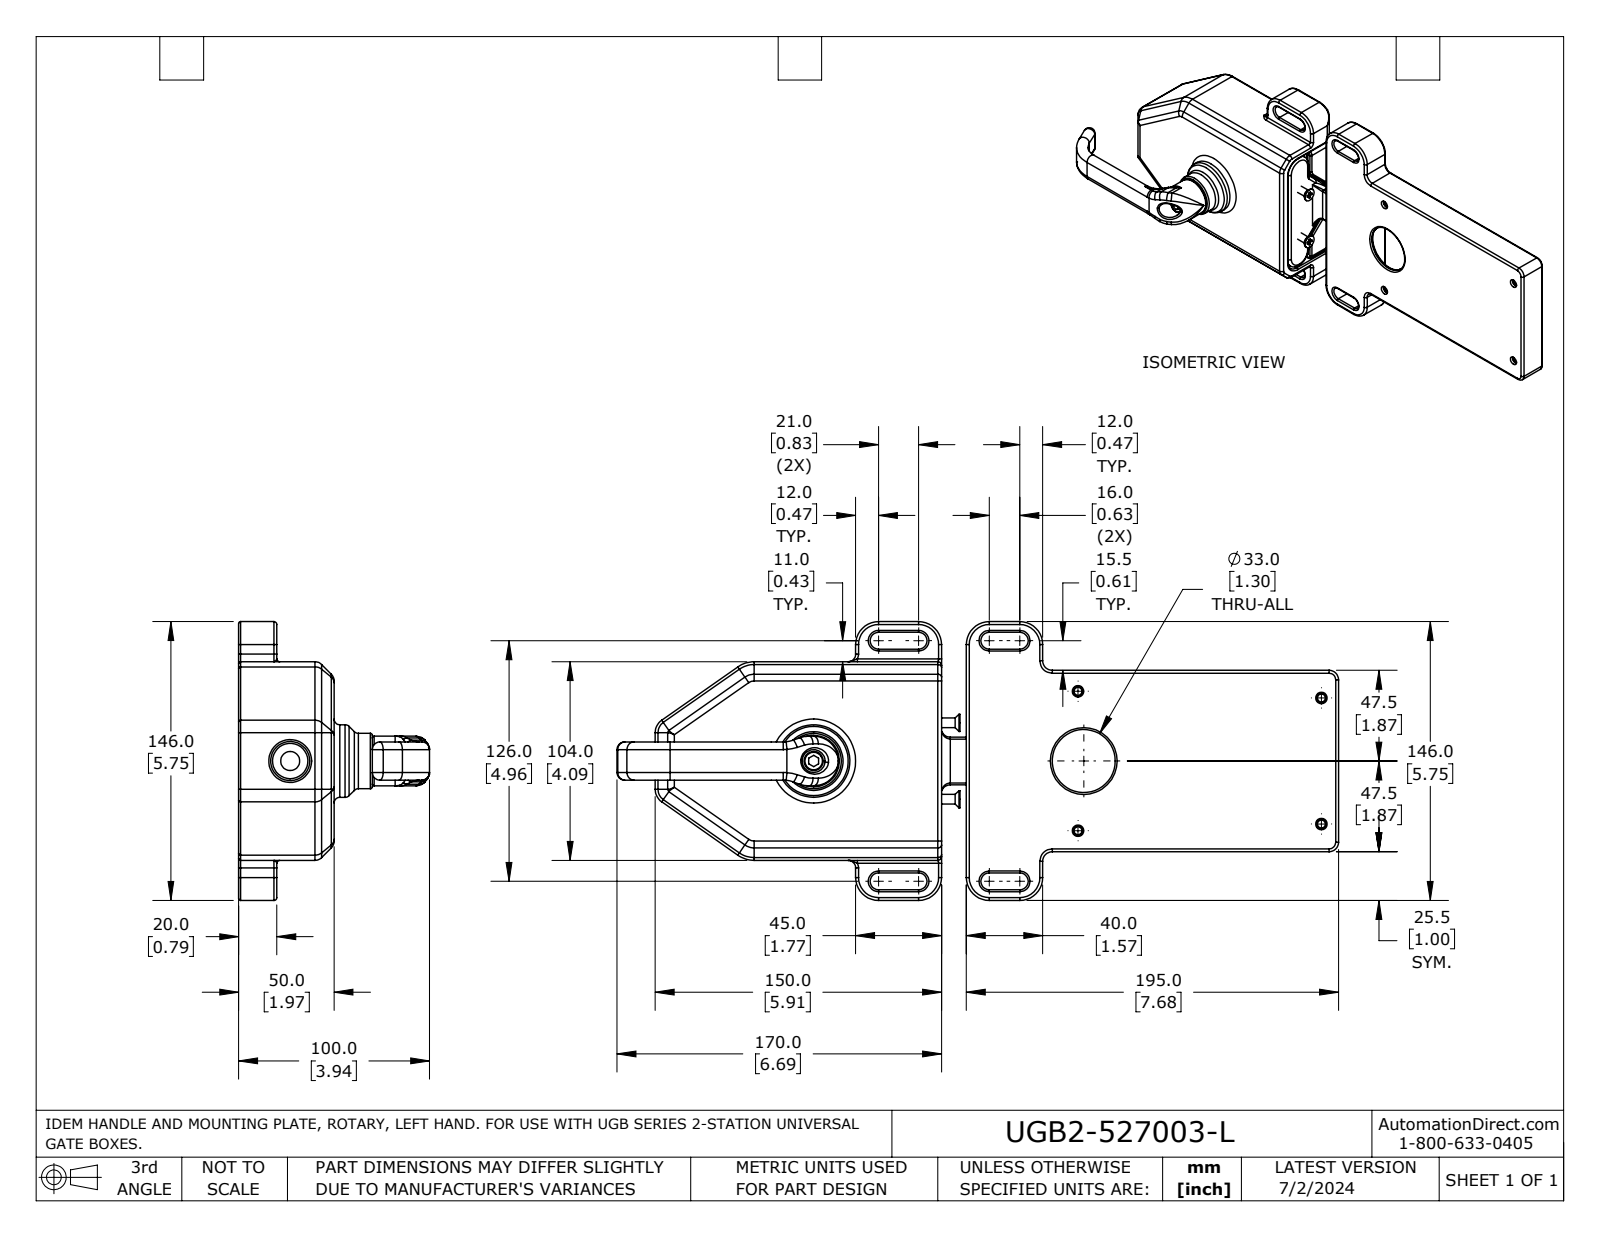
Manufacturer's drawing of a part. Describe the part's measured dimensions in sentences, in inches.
The part is named "UGB2-527003 -L". Its 3-D file was written by "SolidWorks 2023 (AUTOMOTIVE_DESIGN)". It is 6 solids with 1652 faces: 379 planar, 654 cylindrical and 619 other. Overall it measures 14.882 by 5.748 by 3.937 inches. Its volume is 28.11 cubic inches and its surface area 340.3 square inches. Round holes: 10 of diameter 0.165, 4 of diameter 0.217, 4 of diameter 0.236, 2 of diameter 0.13, 2 of diameter 0.413, 1 of diameter 0.248, 1 of diameter 0.268, 1 of diameter 0.472, 1 of diameter 0.559, 1 of diameter 0.827, 1 of diameter 0.906, 1 of diameter 1.165. Round bosses or shafts: 4 of diameter 0.335, 4 of diameter 0.197, 4 of diameter 0.173, 2 of diameter 0.787, 2 of diameter 0.354, 2 of diameter 0.276, 2 of diameter 0.199, 1 of diameter 1.496. Partial cylindrical surfaces (rounded edges, fillets, slot ends): 259 of radius 0.039, 90 of radius 0.079, 28 of radius 0.197, 24 of radius 0.118, 19 of radius 0.031, 12 of radius 0.02, 12 of radius 0.157, 11 of radius 0.059. The main face-to-face distances are 0.098, 0.65, 0.138, 0.039, 0.748, 1.929, 1.831, 0.551, 1.693, 1.28. The hole center spacings are 0.812, 1.442, 1.562, 2.195, 2.665, 3.295, 3.645, 3.744.
